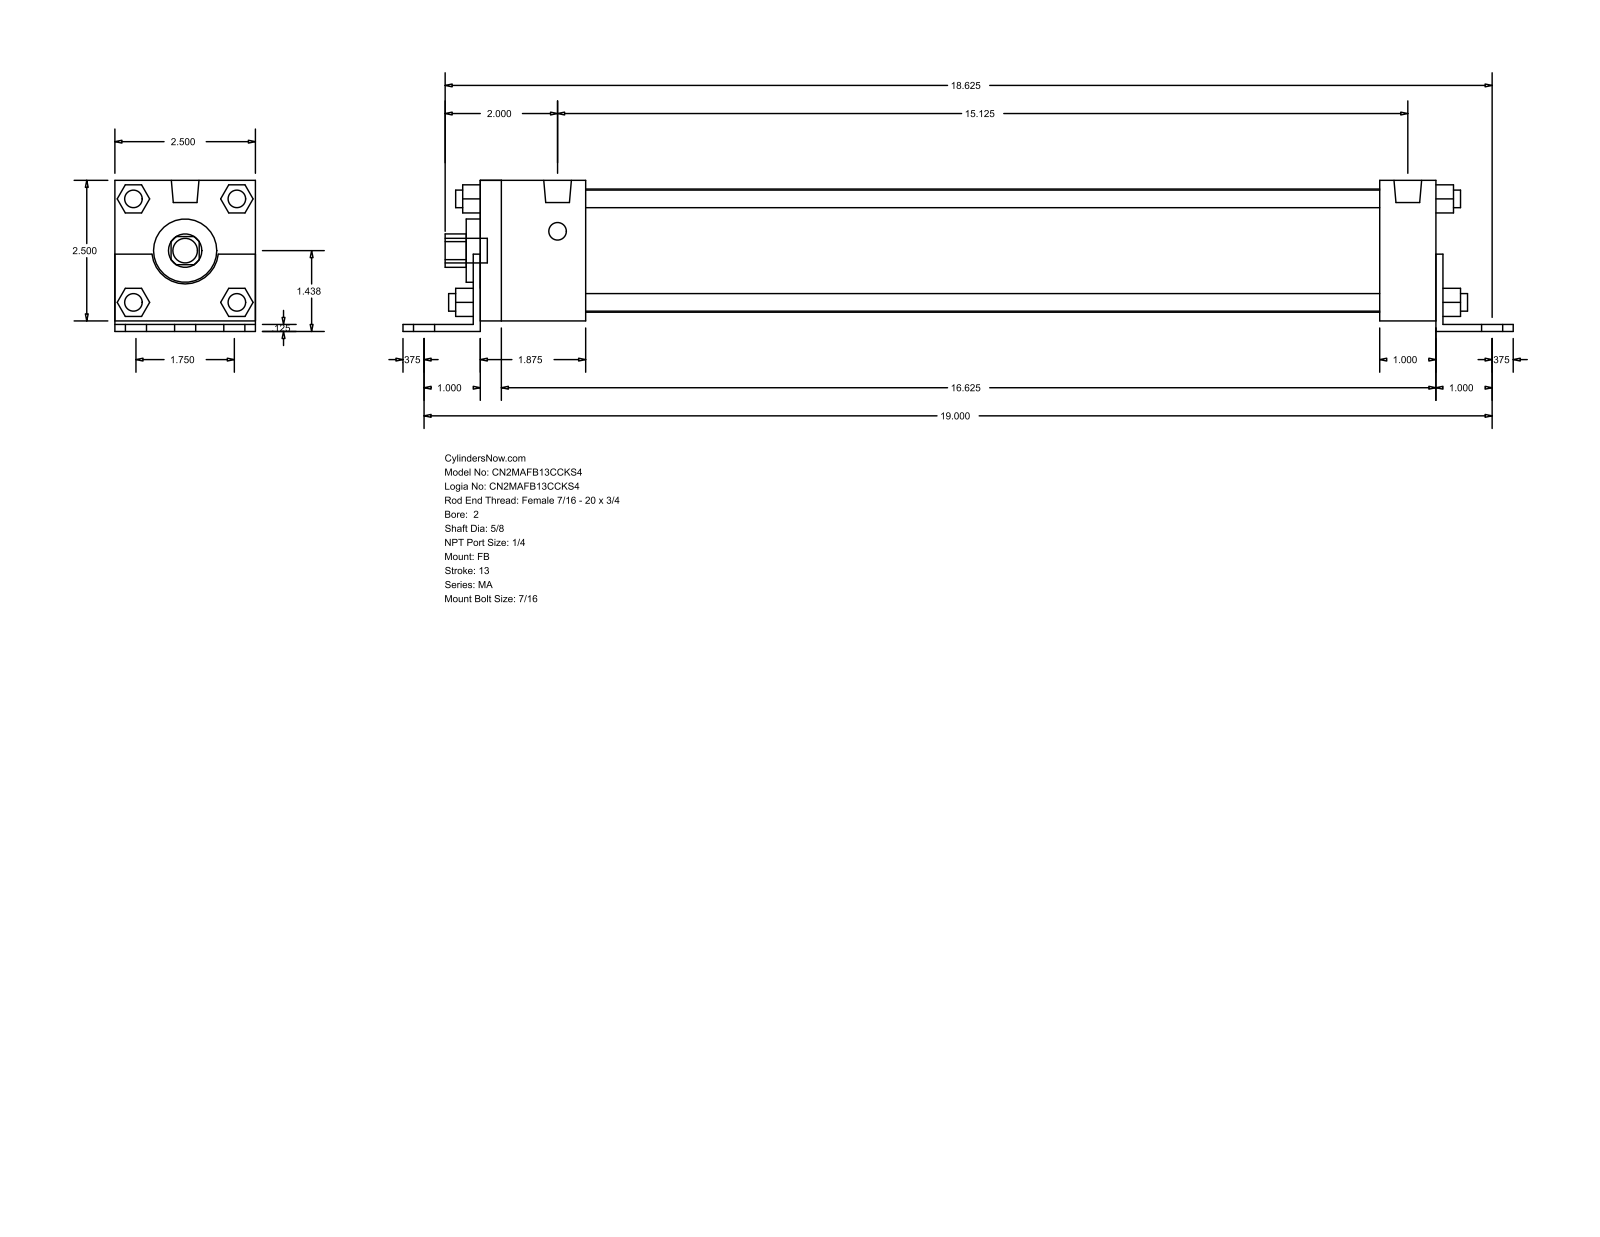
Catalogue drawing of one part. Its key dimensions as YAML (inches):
part_name: "MA_FB__0200_0.625"
step_written_by: "GSSL Pune (CONFIG_CONTROL_DESIGN)"
units: inches
bodies: {solids: 0, faces: 140, planar: 105, cylindrical: 35, other: 0}
overall_size: [19.75, 2.687, 2.5]
round_holes:
  - {diameter: 0.625, count: 1}
  - {diameter: 1.125, count: 1}
  - {diameter: 2.19, count: 1}
round_bosses_or_shafts:
  - {diameter: 0.313, count: 8}
  - {diameter: 0.437, count: 7}
  - {diameter: 0.492, count: 2}
partial_cylinders:
  - {radius: 0.297, count: 1}
  - {radius: 0.593, count: 1}
face_to_face_distances: [2.5, 0.125, 0.187, 2.687, 0.063, 2.563, 17, 17.25, 0.125, 17.125]
